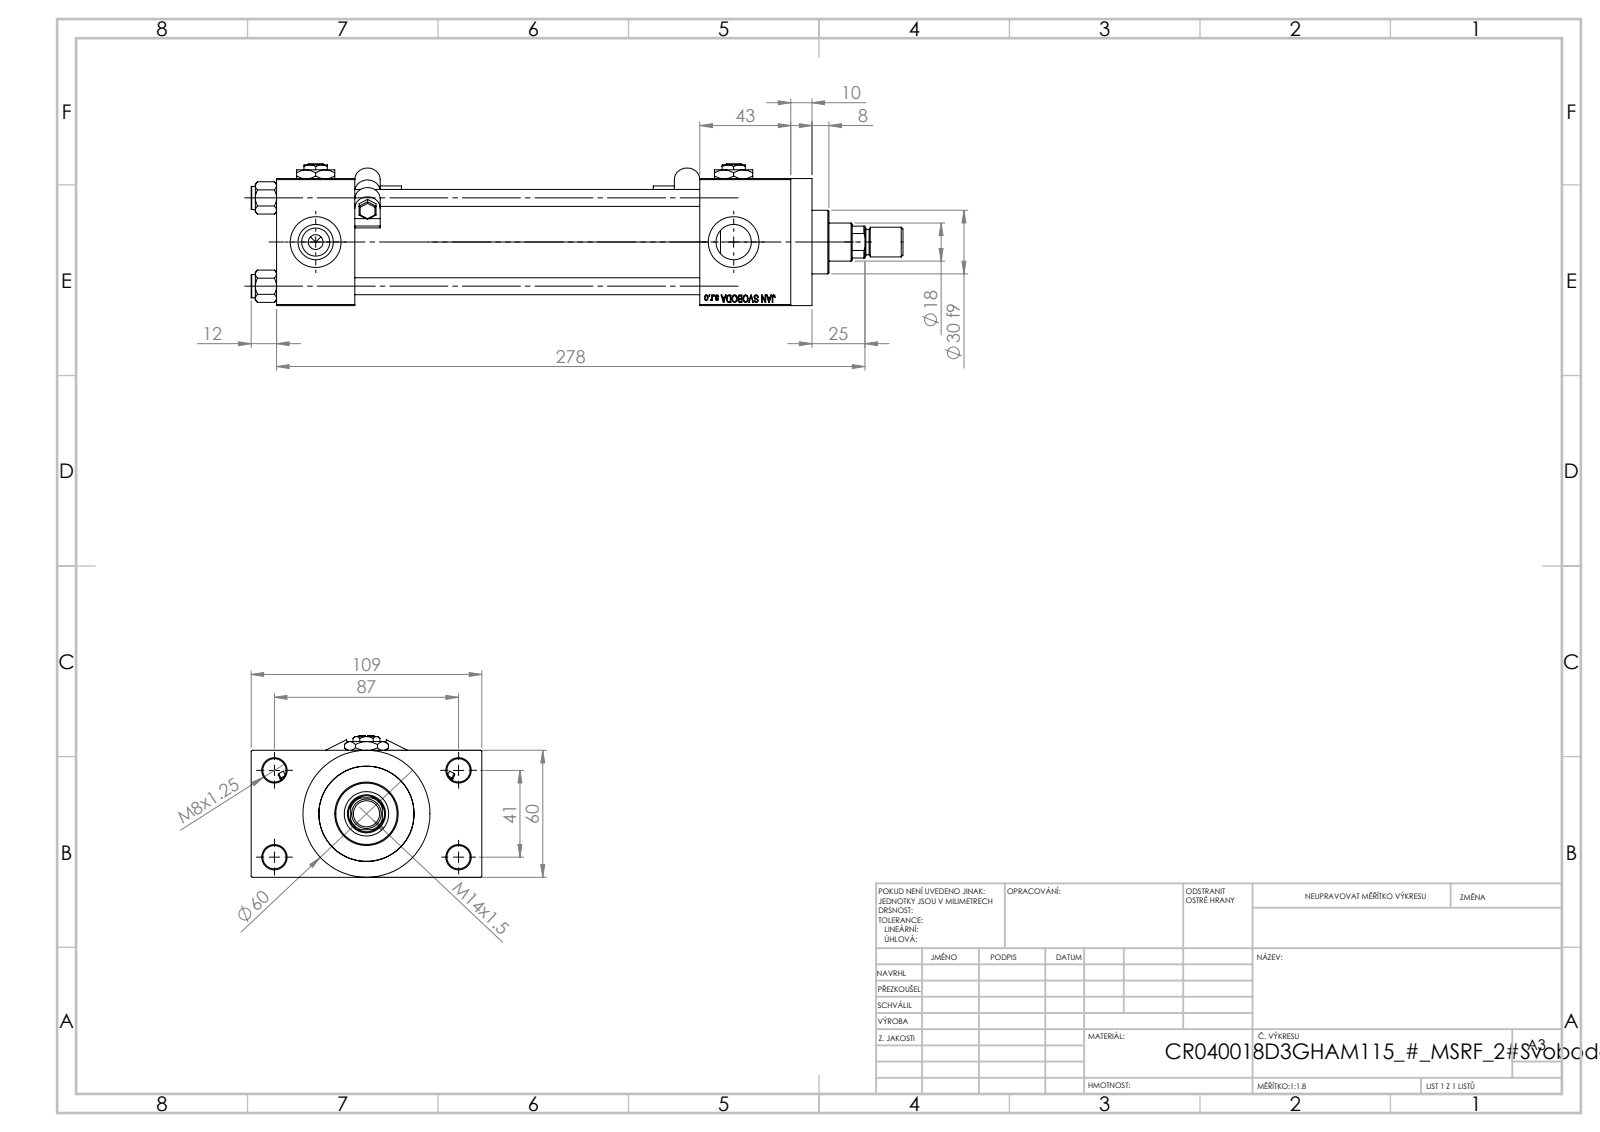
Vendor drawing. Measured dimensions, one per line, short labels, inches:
name: V215CR_D_Body; Zatka_pro_OIL_PORT; NUT_M5_D; V215CR_VCP_D (+4 more)
written by: SolidWorks 2019 (CONFIG_CONTROL_DESIGN)
unit: in
bodies: 16 solids, 1283 faces (586 planar, 131 cylindrical, 566 other)
size: 12.126 × 4.291 × 2.638
volume: 37.25 in³; area: 272 in²
holes: 4× ⌀0.315, 4× ⌀0.433, 4× ⌀0.656, 4× ⌀0.945, 3× ⌀0.276, 1× ⌀0.335, 1× ⌀0.709, 1× ⌀0.827, 1× ⌀1.22, 1× ⌀1.575, 1× ⌀1.772
bosses: 4× ⌀0.433, 2× ⌀0.197, 2× ⌀0.098, 1× ⌀2.362, 1× ⌀1.811, 1× ⌀1.181, 1× ⌀0.551, 1× ⌀0.472
rounds: 12× R0.02, 4× R0.236, 1× R0.335
face distances: 2.362, 6.417, 0.965, 7.874, 3.327, 1.457, 1.693, 9.567, 8.11, 2.087
hole spacings: 0.892, 1.161, 1.642, 1.856, 1.893, 2.533, 3.011, 1.614
